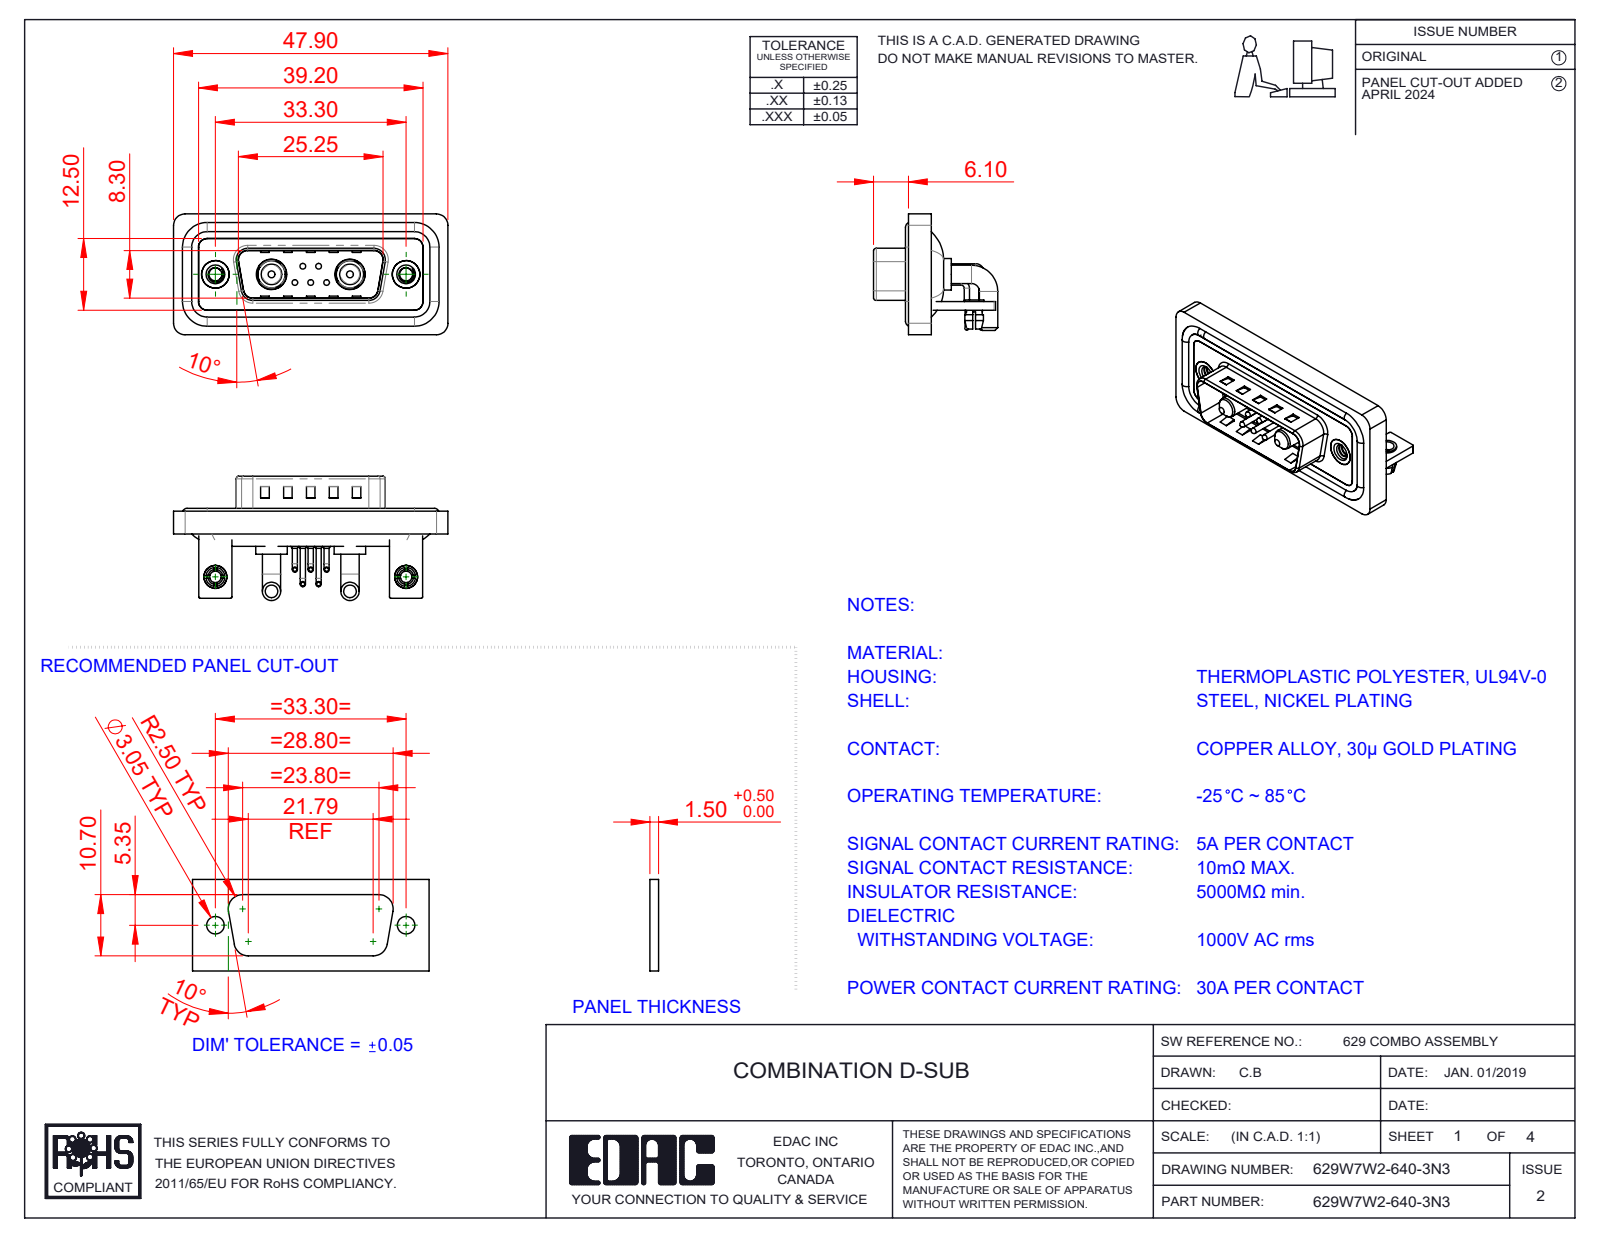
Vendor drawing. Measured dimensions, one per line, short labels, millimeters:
name: 629Combo Shell Front_15 Contacts; 629Combo Shell Rear_15 Contacts; 629Combo Stabilizer Bracket; 629Combo Waterproof Housing_15 Contacts (+7 more)
written by: SolidWorks 2023 (CONFIG_CONTROL_DESIGN)
unit: mm
bodies: 20 solids, 1215 faces (585 planar, 456 cylindrical, 174 other)
size: 47.9 × 21.7 × 21.1
volume: 6 050 mm³; area: 9 975 mm²
holes: 7× ⌀2, 5× ⌀0.75, 5× ⌀1.6, 2× ⌀2.26, 2× ⌀2.5, 2× ⌀3.2, 2× ⌀4, 2× ⌀4.8, 2× ⌀4.85, 2× ⌀5, 2× ⌀5.3
bosses: 10× ⌀0.9, 5× ⌀1.5, 5× ⌀1, 5× ⌀0.65, 4× ⌀3.2, 4× ⌀1.6, 2× ⌀5.5, 2× ⌀5.2
rounds: 21× R2, 18× R1.5, 16× R0.25, 9× R0.5, 8× R1.6, 5× R1.01, 4× R0.6, 4× R0.65
face distances: 0.4, 1.5, 0.8, 2.9, 2.1, 1.1, 1.6, 1.2, 3.7, 4.5
hole spacings: 3.16, 2.77, 9.8, 23.5, 33.3, 4.31, 4.33, 5.03
